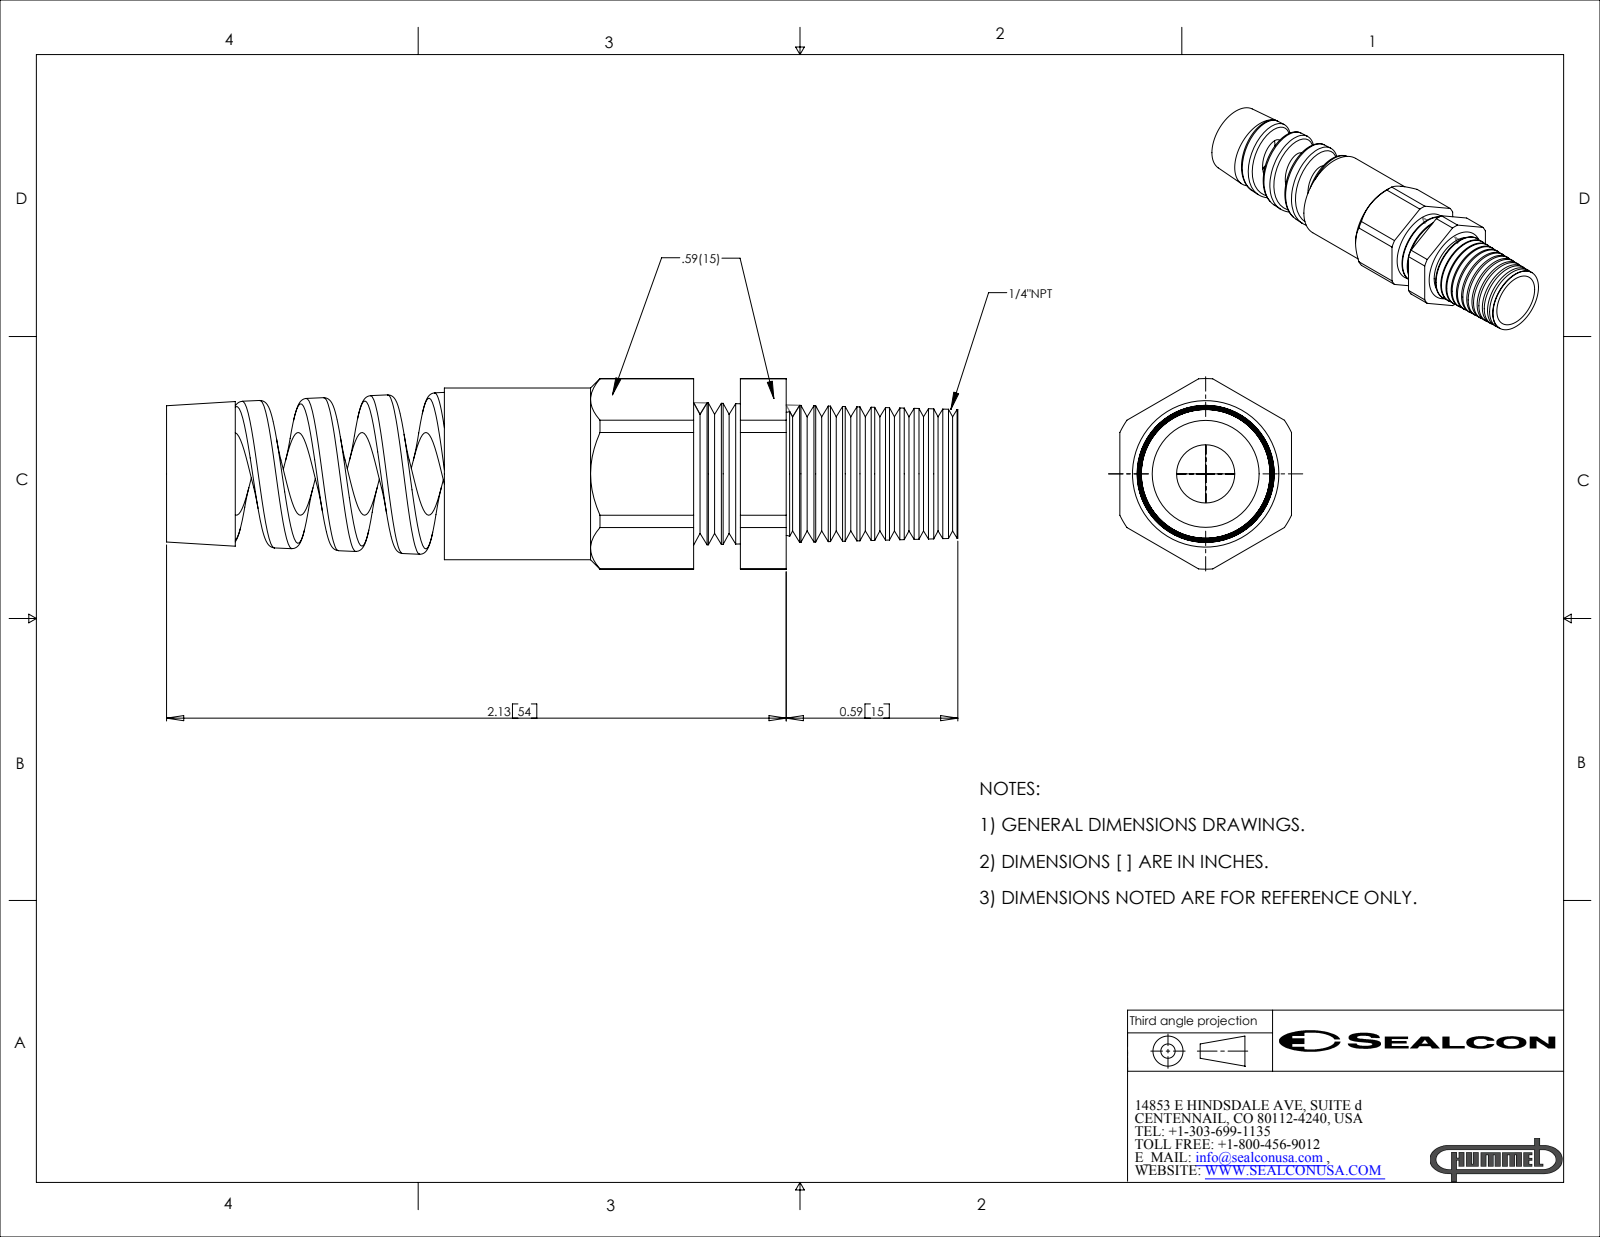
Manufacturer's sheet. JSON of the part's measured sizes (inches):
{"part_name": "CF07CR-BK", "step_written_by": "SolidWorks 2007 (CONFIG_CONTROL_DESIGN)", "units": "inches", "bodies": {"solids": 2, "faces": 177, "planar": 24, "cylindrical": 33, "other": 120}, "overall_size": [2.72, 0.655, 0.59], "volume_in3": 0.387, "surface_area_in2": 8.877, "round_holes": [[0.2, 1], [0.284, 1], [0.313, 1]], "round_bosses_or_shafts": [[0.59, 1], [0.367, 1]], "partial_cylinders_radius": [[0.327, 1]], "face_to_face_distances": [0.59, 0.515, 0.502, 1.018, 0.157, 0.673, 0.857, 0.354, 0.161, 1.175]}
